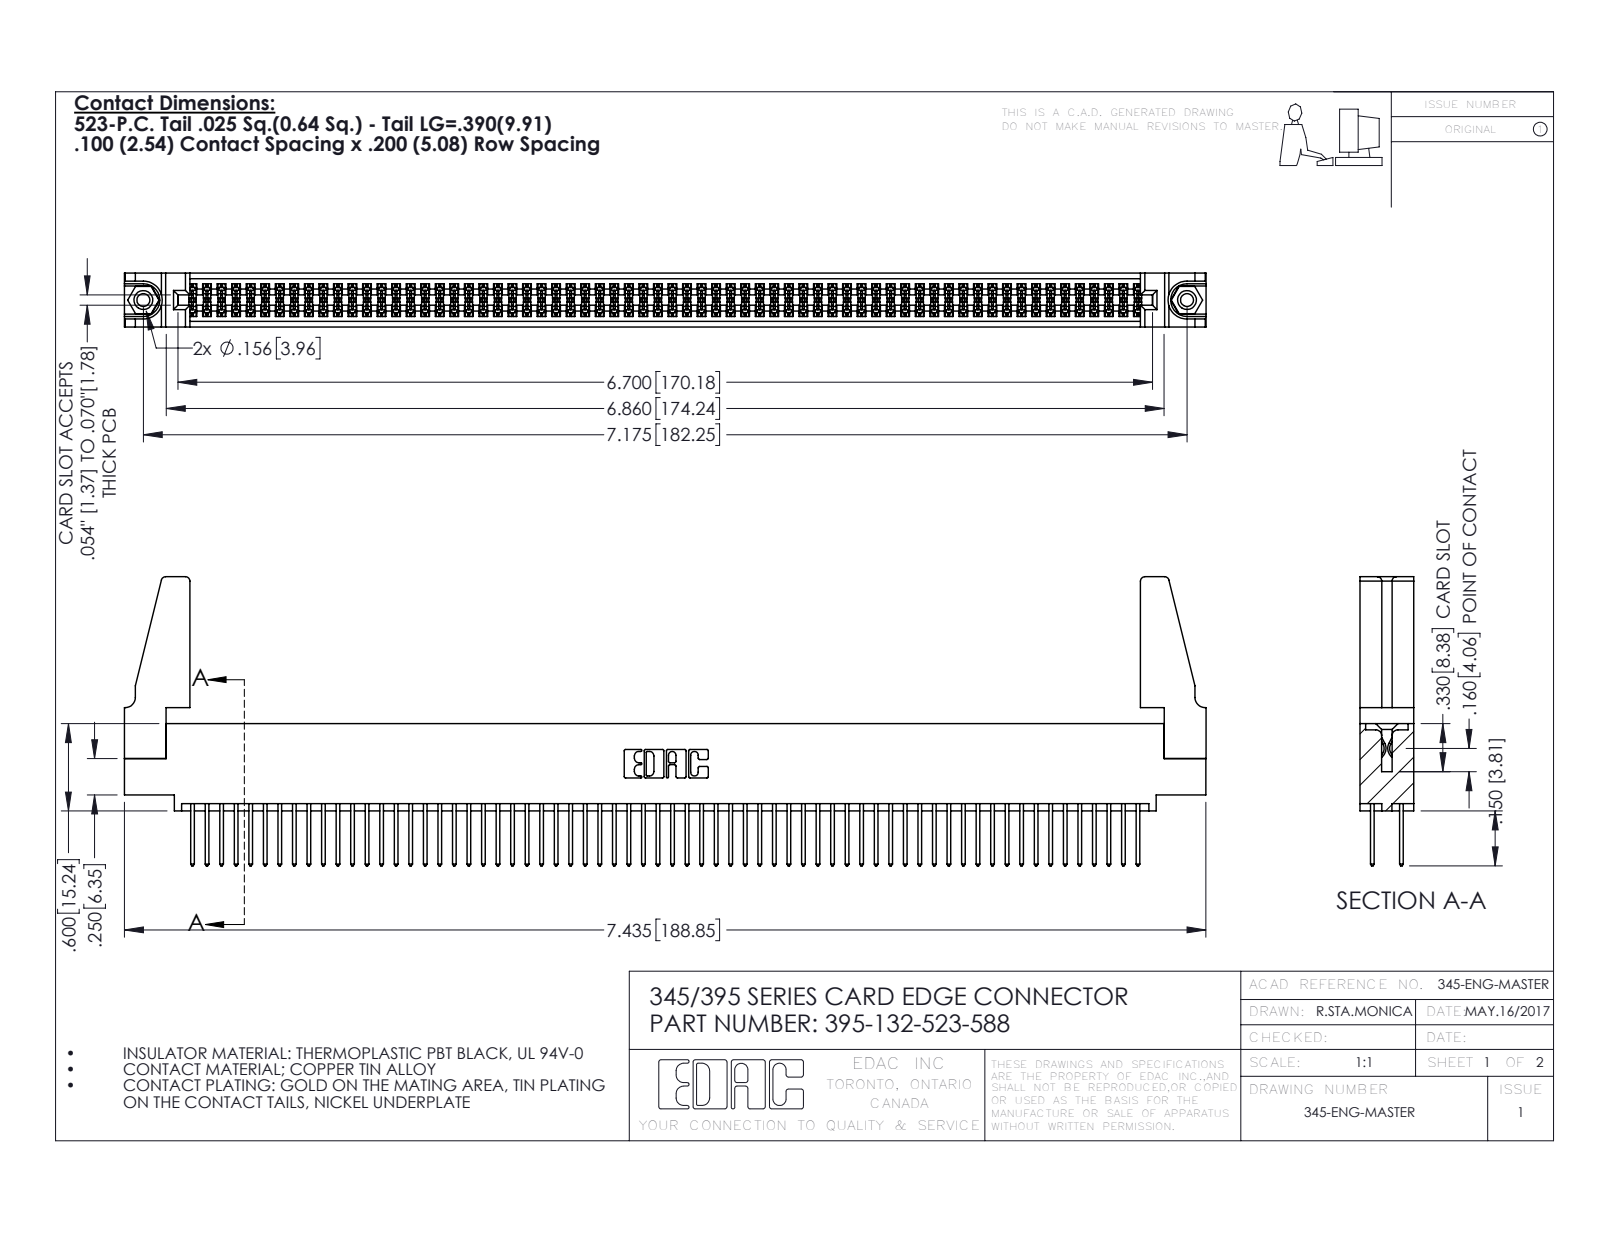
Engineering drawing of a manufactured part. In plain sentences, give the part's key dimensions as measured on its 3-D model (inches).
The part is named "345-250-001_345-250-001-102; 345 Part_0.110 Offset - 0.156 Dia-TH; 345-292-001_345-293-123; 345-220-078_345-220-088 (+1 more)". Its 3-D file was written by "SolidWorks 2016 (CONFIG_CONTROL_DESIGN)". It is 137 solids with 6854 faces: 4512 planar, 2326 cylindrical and 16 other. Overall it measures 7.436 by 1.987 by 0.37 inches. Its volume is 1.344 cubic inches and its surface area 50.58 square inches. Round holes: 2 of diameter 0.089, 2 of diameter 0.125, 2 of diameter 0.156, 1 of diameter 0.064. Round bosses or shafts: 2 of diameter 0.155. Partial cylindrical surfaces (rounded edges, fillets, slot ends): 198 of radius 0.006, 132 of radius 0.01, 22 of radius 0.01, 8 of radius 0.03, 6 of radius 0.007, 6 of radius 0.031, 3 of radius 0.026, 2 of radius 0.014. The main face-to-face distances are 0.072, 0.298, 0.098, 0.272, 0.025, 0.2, 0.37, 0.225, 0.175, 0.149. The hole center spacings are 0.27, 6.939, 7.175.
